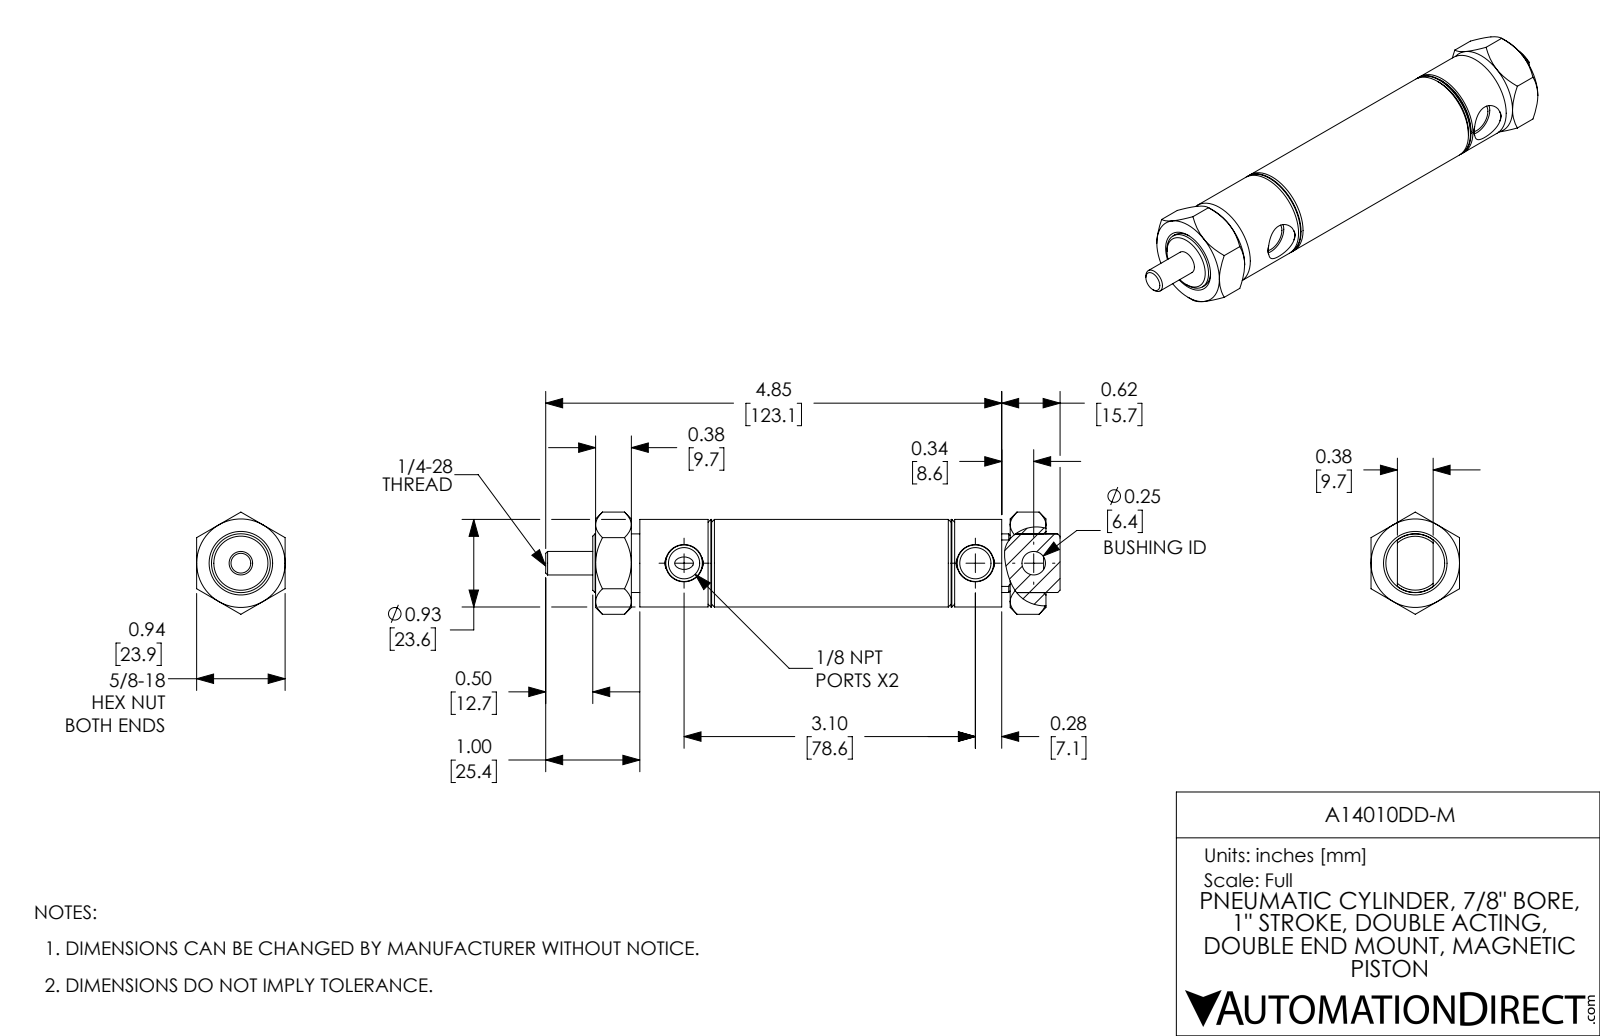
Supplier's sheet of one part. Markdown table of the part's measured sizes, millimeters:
| quantity | value |
| --- | --- |
| part name | A14010DD-M; A14010DD-M_Mounting Nut_D-9; A14010DD-M-Rod; A14010DD-M-MainBody |
| STEP written by | SolidWorks 2017 (AUTOMOTIVE_DESIGN) |
| units | millimeters |
| bodies | 4 solids, 137 faces (35 planar, 38 cylindrical, 64 other) |
| overall size | 138.8 × 27.6 × 23.9 |
| volume | 42 930 mm³ |
| surface area | 21 480 mm² |
| round holes (diameter × count) | 6.4 × 2, 8.4 × 2, 15.9 × 1, 22.2 × 1 |
| round bosses / shafts (diameter × count) | 23.6 × 1, 15.8 × 1, 14.3 × 1 |
| main face-to-face distances | 23.9, 12.7, 99.9, 2.3, 11.9, 109.6, 111.9, 9.7, 25.4, 70.7 |
| hole center spacings | 15.7, 78.6, 94.4 |
